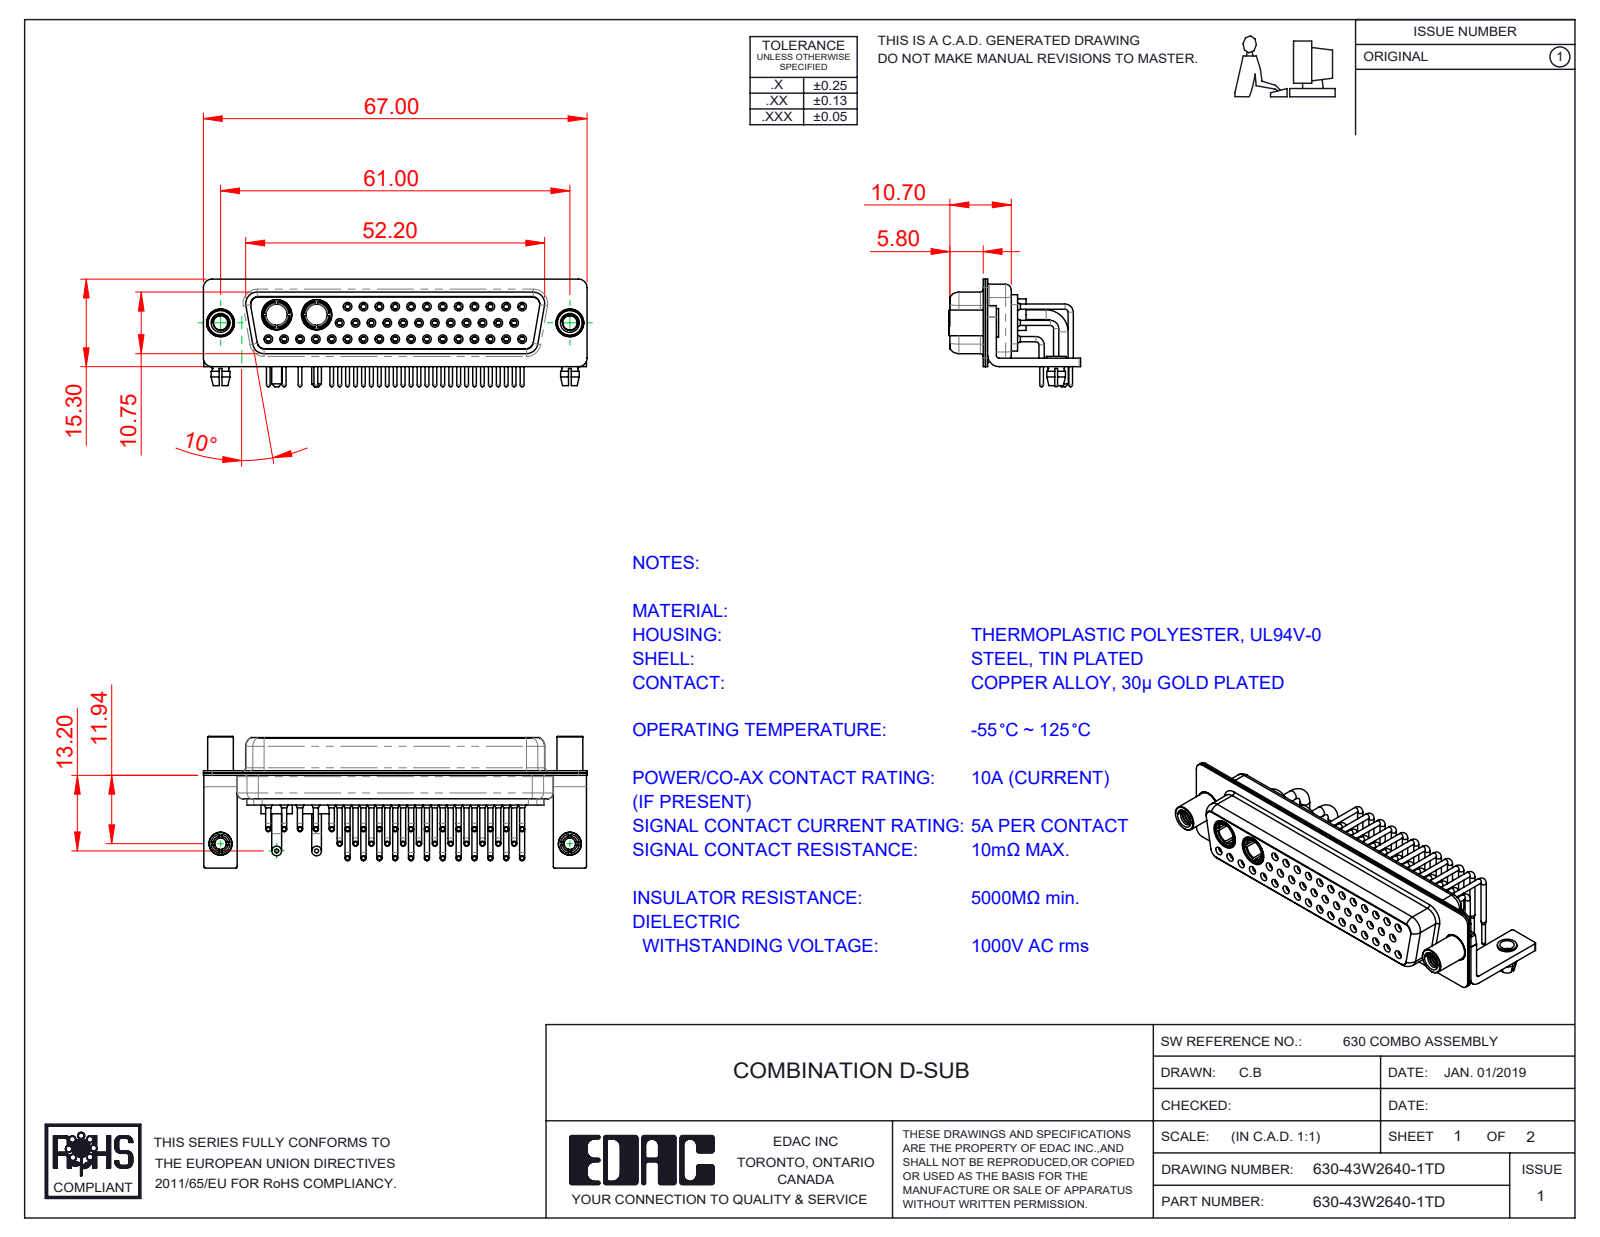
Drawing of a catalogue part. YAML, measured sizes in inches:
part_name: "630Combo Contact Row 3; 630Combo Contact Row 1_50 Contacts; 630Combo Stabilizer Bracket_50 Contacts; 630Combo Board Lock_50 Contacts (+7 more)"
step_written_by: "SolidWorks 2020 (CONFIG_CONTROL_DESIGN)"
units: inches
bodies: {solids: 54, faces: 2798, planar: 810, cylindrical: 1234, other: 754}
overall_size: [2.638, 0.906, 0.74]
volume: 0.463
surface_area: 26.34
round_holes:
  - {diameter: 0.079, count: 43}
  - {diameter: 0.035, count: 41}
  - {diameter: 0.043, count: 41}
  - {diameter: 0.059, count: 41}
  - {diameter: 0.063, count: 29}
  - {diameter: 0.067, count: 12}
  - {diameter: 0.098, count: 4}
  - {diameter: 0.191, count: 4}
  - {diameter: 0.126, count: 2}
  - {diameter: 0.146, count: 2}
  - {diameter: 0.157, count: 2}
  - {diameter: 0.159, count: 2}
round_bosses_or_shafts:
  - {diameter: 0.035, count: 41}
  - {diameter: 0.026, count: 41}
  - {diameter: 0.063, count: 12}
  - {diameter: 0.067, count: 4}
  - {diameter: 0.217, count: 2}
  - {diameter: 0.205, count: 2}
  - {diameter: 0.197, count: 2}
  - {diameter: 0.195, count: 2}
partial_cylinders:
  - {radius: 0.01, count: 16}
  - {radius: 0.059, count: 16}
  - {radius: 0.079, count: 13}
  - {radius: 0.053, count: 12}
  - {radius: 0.063, count: 8}
  - {radius: 0.02, count: 5}
  - {radius: 0.024, count: 4}
  - {radius: 0.026, count: 4}
face_to_face_distances: [0.016, 0.059, 0.236, 0.22, 0.031, 0.205, 0.228, 0.444, 0.072, 0.244]
hole_center_spacings: [0.109, 0.124, 0.218, 0.327, 0.436, 0.545, 0.654, 0.763]
